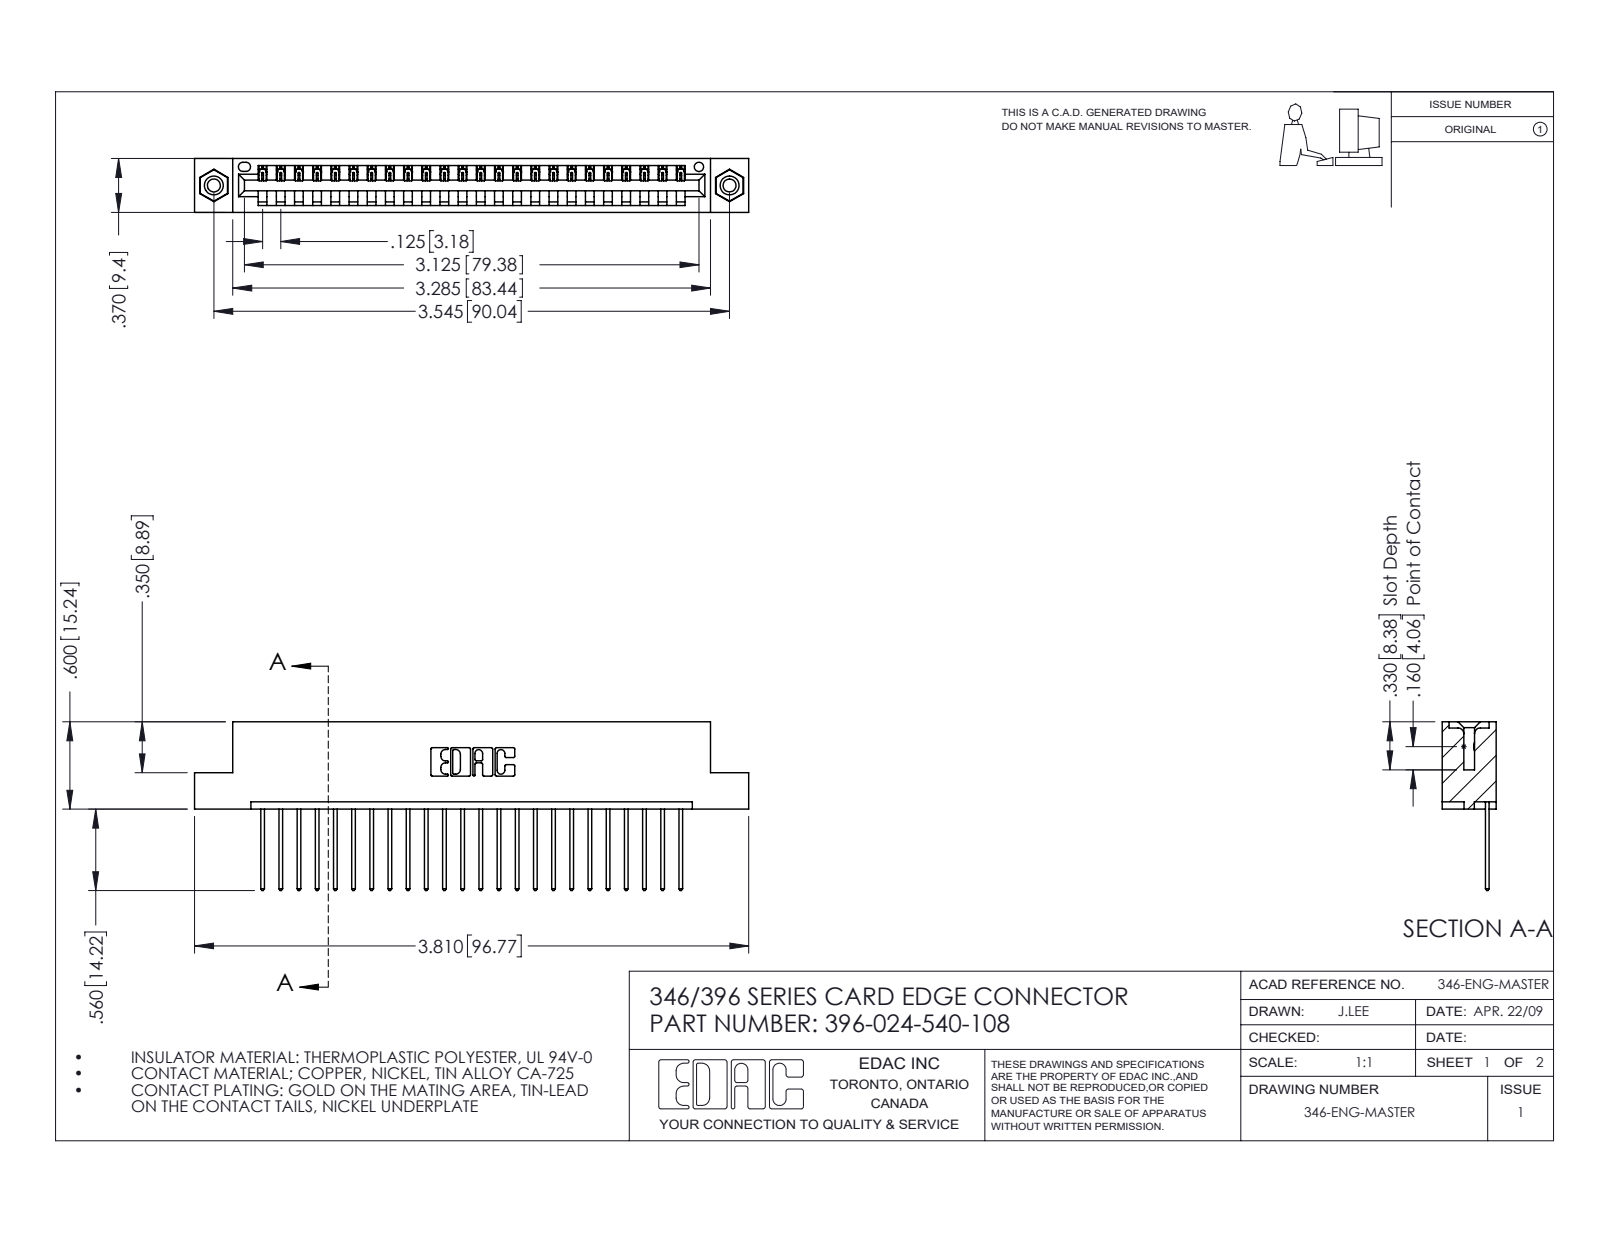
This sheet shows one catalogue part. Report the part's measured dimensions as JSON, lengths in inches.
{"part_name": "345-292-001_345-293-140; 345-250-001_345-250-003-102; 346 Part_Flush Mounting Lugs - 0.156 Dia-TI; 396-024-540-108", "step_written_by": "SolidWorks 2016 (CONFIG_CONTROL_DESIGN)", "units": "inches", "bodies": {"solids": 27, "faces": 1574, "planar": 1068, "cylindrical": 490, "other": 16}, "overall_size": [3.81, 1.16, 0.37], "volume_in3": 0.559, "surface_area_in2": 17.86, "round_holes": [[0.089, 2], [0.125, 2], [0.156, 2], [0.064, 1]], "round_bosses_or_shafts": [[0.155, 2]], "partial_cylinders_radius": [[0.006, 48], [0.01, 48], [0.01, 22], [0.007, 6], [0.031, 6], [0.026, 3], [0.031, 2], [0.04, 2]], "face_to_face_distances": [0.048, 0.322, 0.25, 0.37, 0.072, 0.298, 0.025, 0.148, 0.222, 0.1], "hole_center_spacings": [0.246, 3.337, 3.545]}
